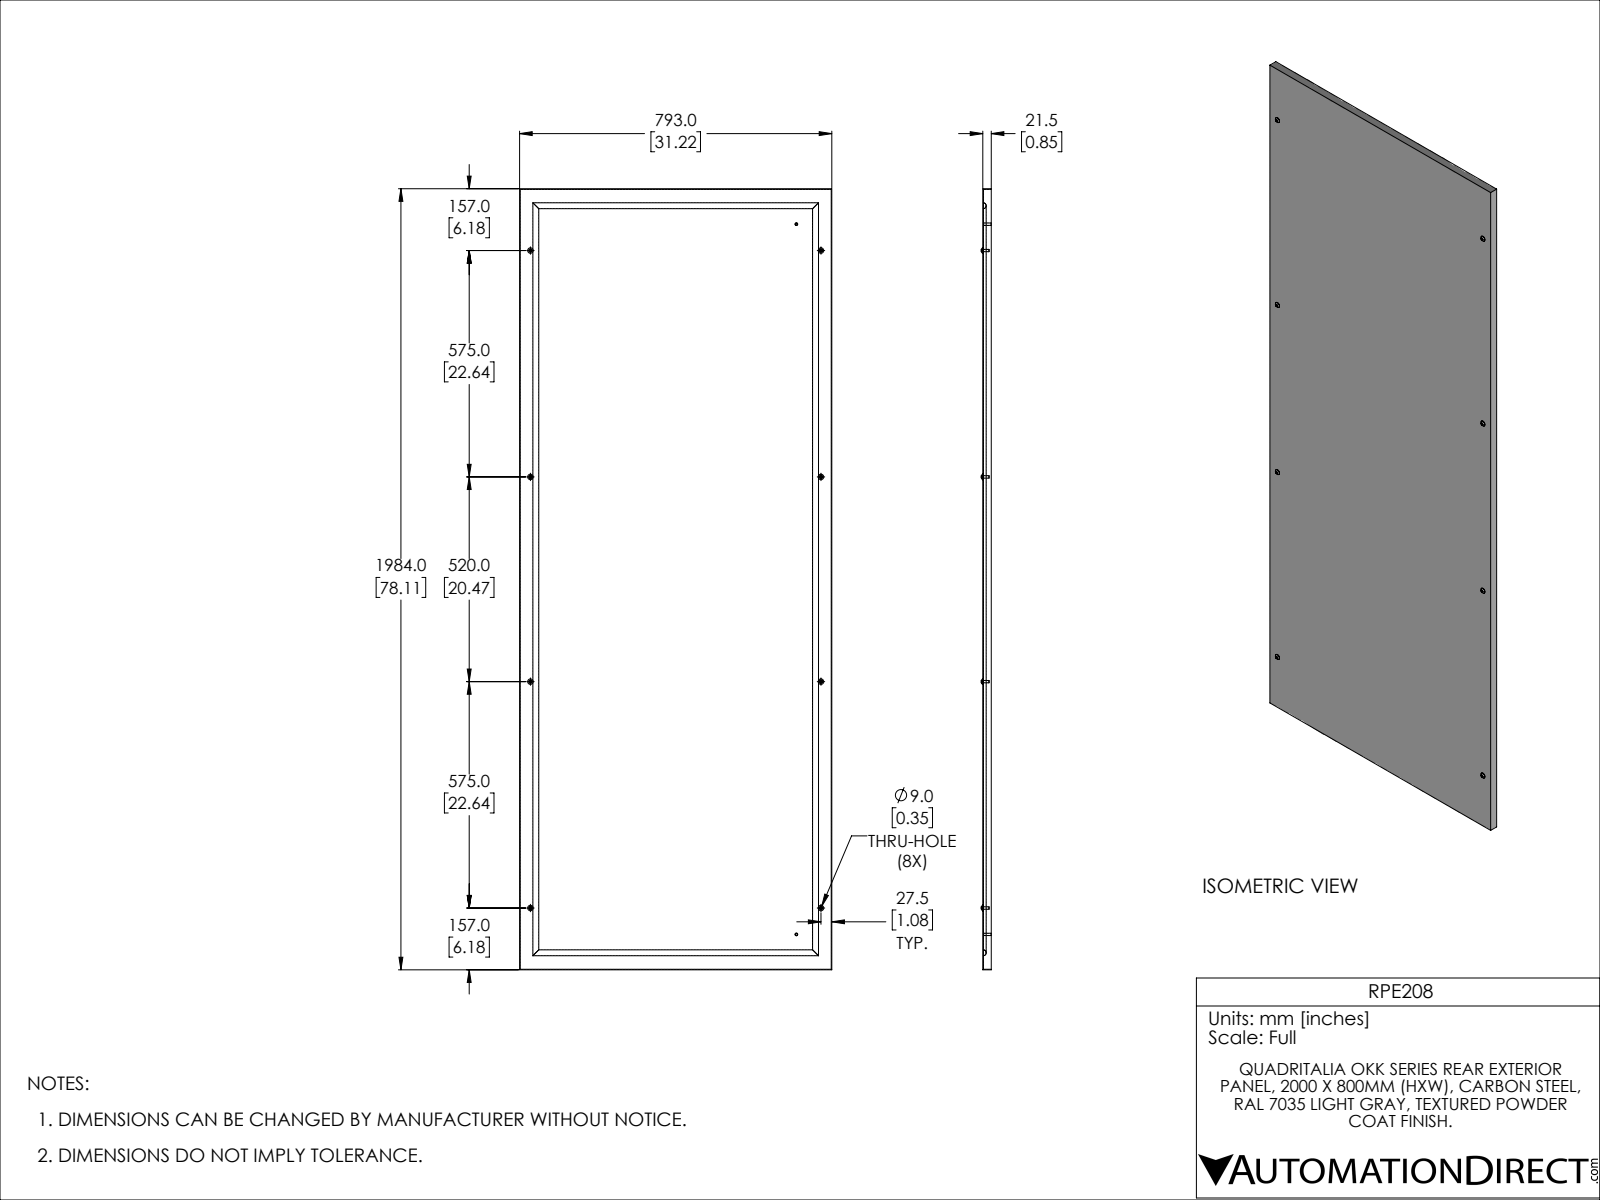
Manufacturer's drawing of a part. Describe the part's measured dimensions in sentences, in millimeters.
The part is named "RPE208". Its 3-D file was written by "SolidWorks 2021 (CONFIG_CONTROL_DESIGN)". It is 15 solids with 311 faces: 157 planar, 128 cylindrical and 26 other. Overall it measures 1984 by 793 by 25.2 millimeters. Its volume is 2 956 000 cubic millimeters and its surface area 3 580 000 square millimeters. Round holes: 8 of diameter 9. Round bosses or shafts: 10 of diameter 6, 8 of diameter 14, 2 of diameter 7. Partial cylindrical surfaces (rounded edges, fillets, slot ends): 96 of radius 0.5, 4 of radius 7.5. The main face-to-face distances are 1.5, 791.5, 793, 790, 1982.5, 1984, 1981, 21.5, 20, 839.2. The hole center spacings are 575, 738, 935.6, 1095, 1320.5, 520, 902.8, 1670.
